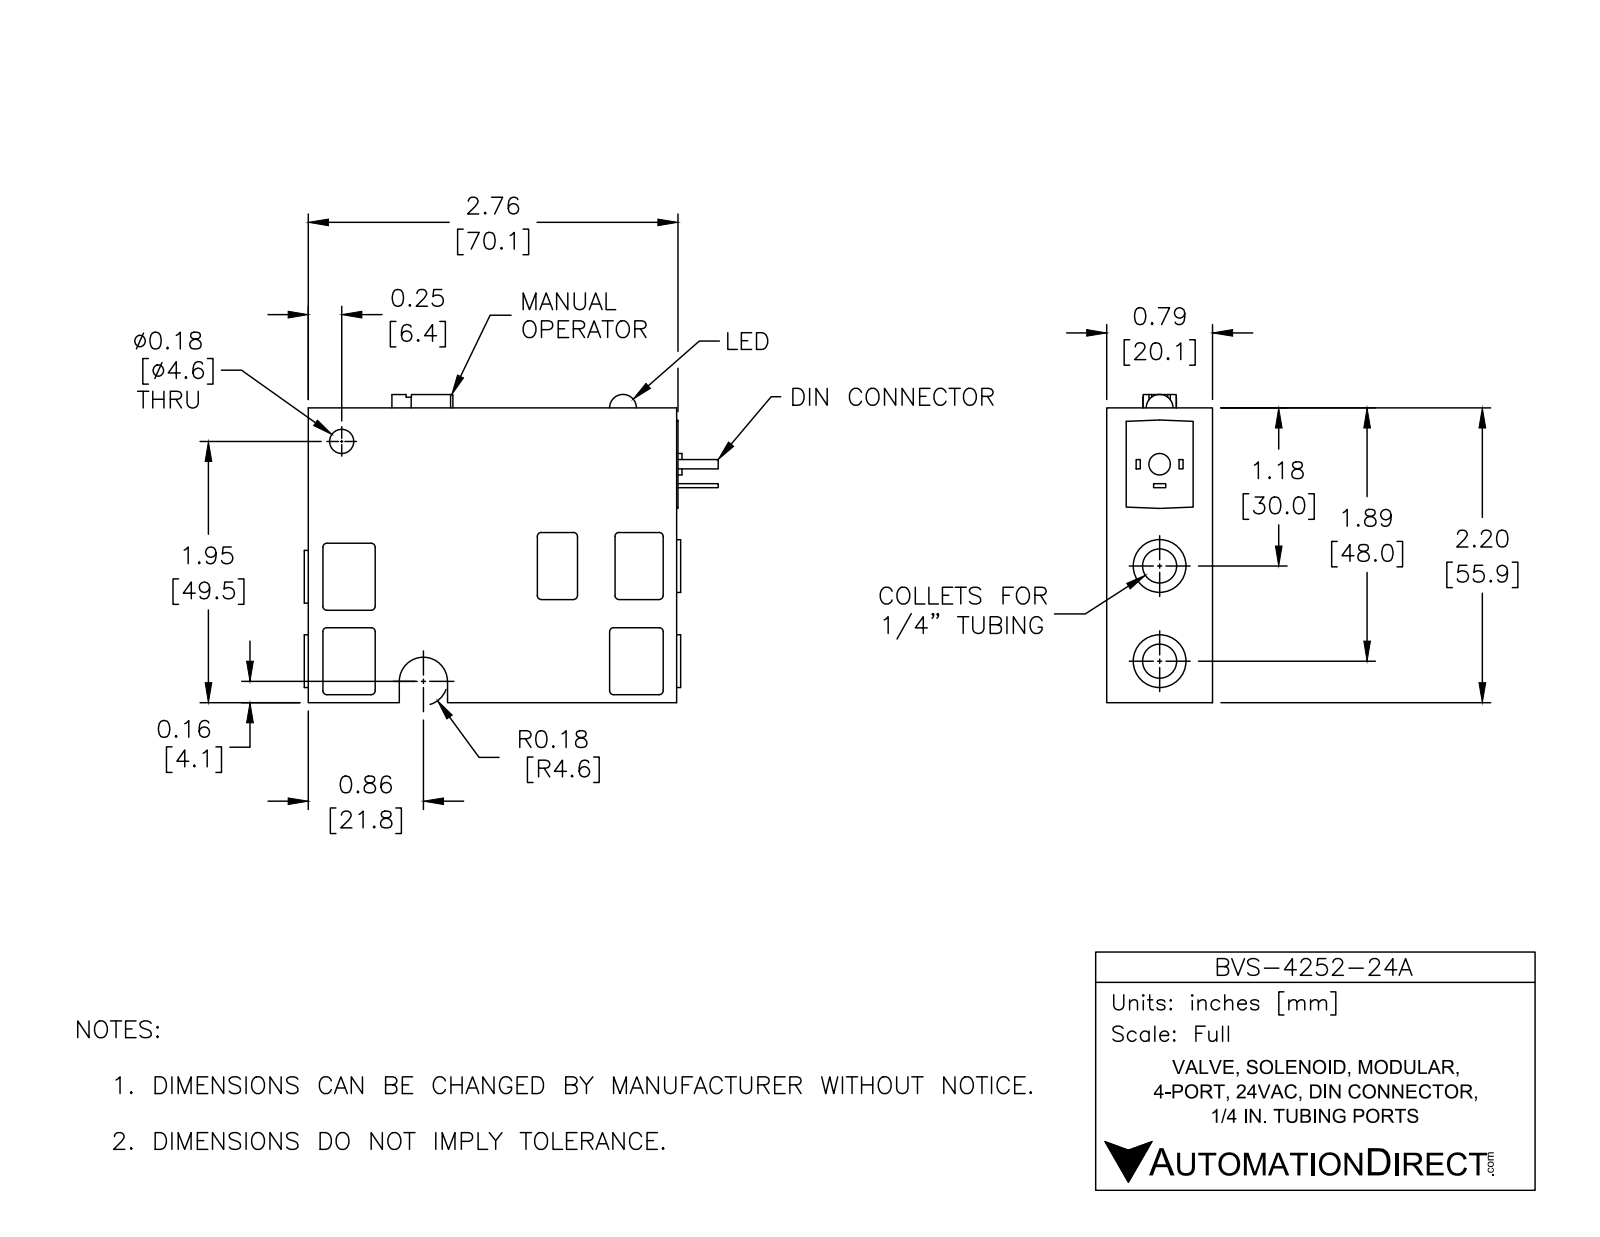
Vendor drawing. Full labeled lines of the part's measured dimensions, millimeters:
Part name (STEP PRODUCT): BVS-4252-24A
STEP written by: SolidWorks 2016 (AUTOMOTIVE_DESIGN)
Units: millimetres
Bodies: 1 solid, 169 faces (99 planar, 68 cylindrical, 2 other)
Overall size (bounding box): 78.5 × 58.4 × 20.1
Volume: 71 680 mm³ · Surface area: 16 250 mm²
Round holes (diameter × count): ⌀6.5 ×3, ⌀2.5 ×1, ⌀4.6 ×1
Round bosses / shafts (diameter × count): ⌀10 ×3, ⌀4.1 ×1
Partial cylindrical surfaces — rounded edges, fillets, slot ends (radius × count): R0.8 ×20, R0.5 ×2, R3.2 ×1, R4.6 ×1
Main face-to-face distances: 20.1, 2.5, 55.9, 17.5, 69.9, 15, 12.7, 2.8, 67.3, 0.8
Hole centre spacings: 2, 14, 16, 16, 18, 32
